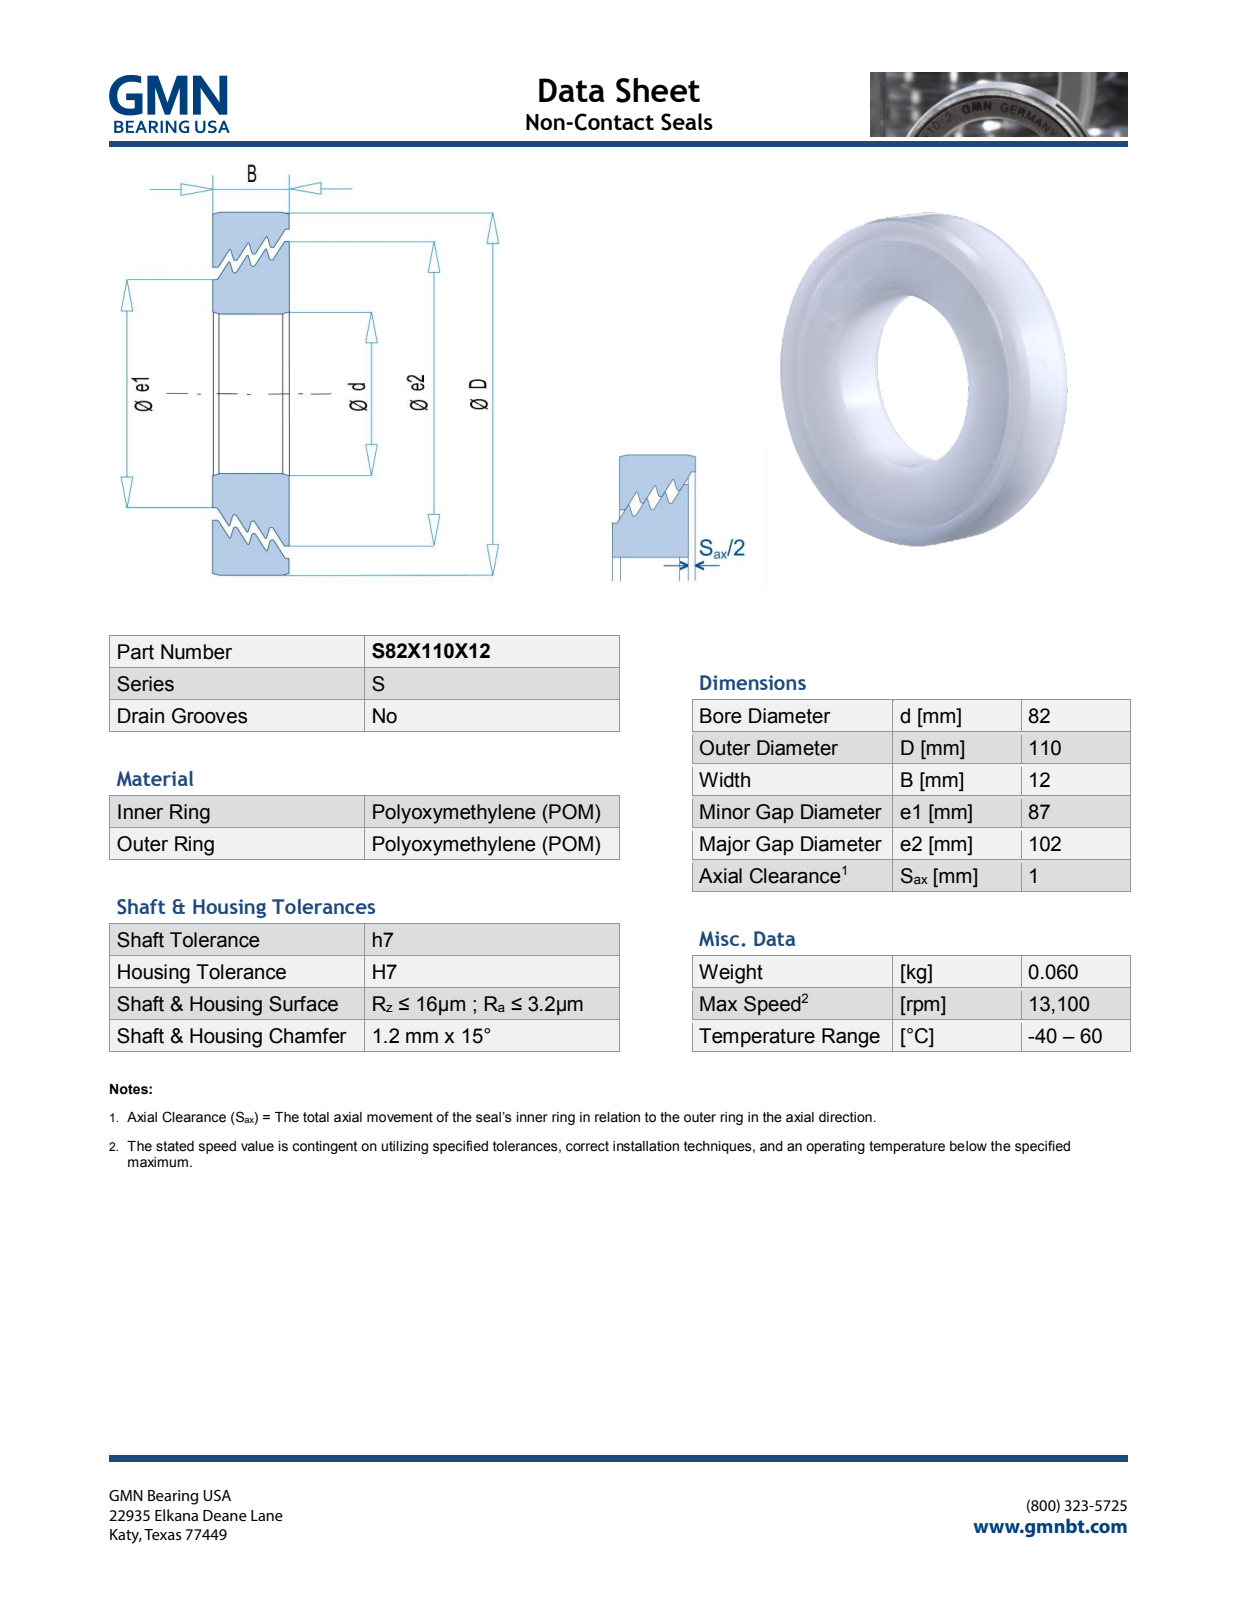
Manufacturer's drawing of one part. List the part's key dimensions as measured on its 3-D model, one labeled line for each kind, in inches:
Part name (STEP PRODUCT): S82X110X12_PRT
STEP written by: PRO/ENGINEER BY PARAMETRIC TECHNOLOGY CORPORATION, 2013150 (AUTOMOTIVE_DESIGN)
Units: inches
Bodies: 2 solids, 636 faces (556 planar, 12 cylindrical, 68 other)
Overall size (bounding box): 4.331 × 4.331 × 0.475
Volume: 2.903 in³ · Surface area: 46.07 in²
Round holes (diameter × count): ⌀3.228 ×1, ⌀3.489 ×1, ⌀4.08 ×1
Round bosses / shafts (diameter × count): ⌀4.331 ×1, ⌀4.016 ×1, ⌀3.425 ×1
Main face-to-face distances: 0.472, 0.475, 0.013, 0.107, 0.014, 0.094, 0.076, 0.081, 0.108, 0.094
